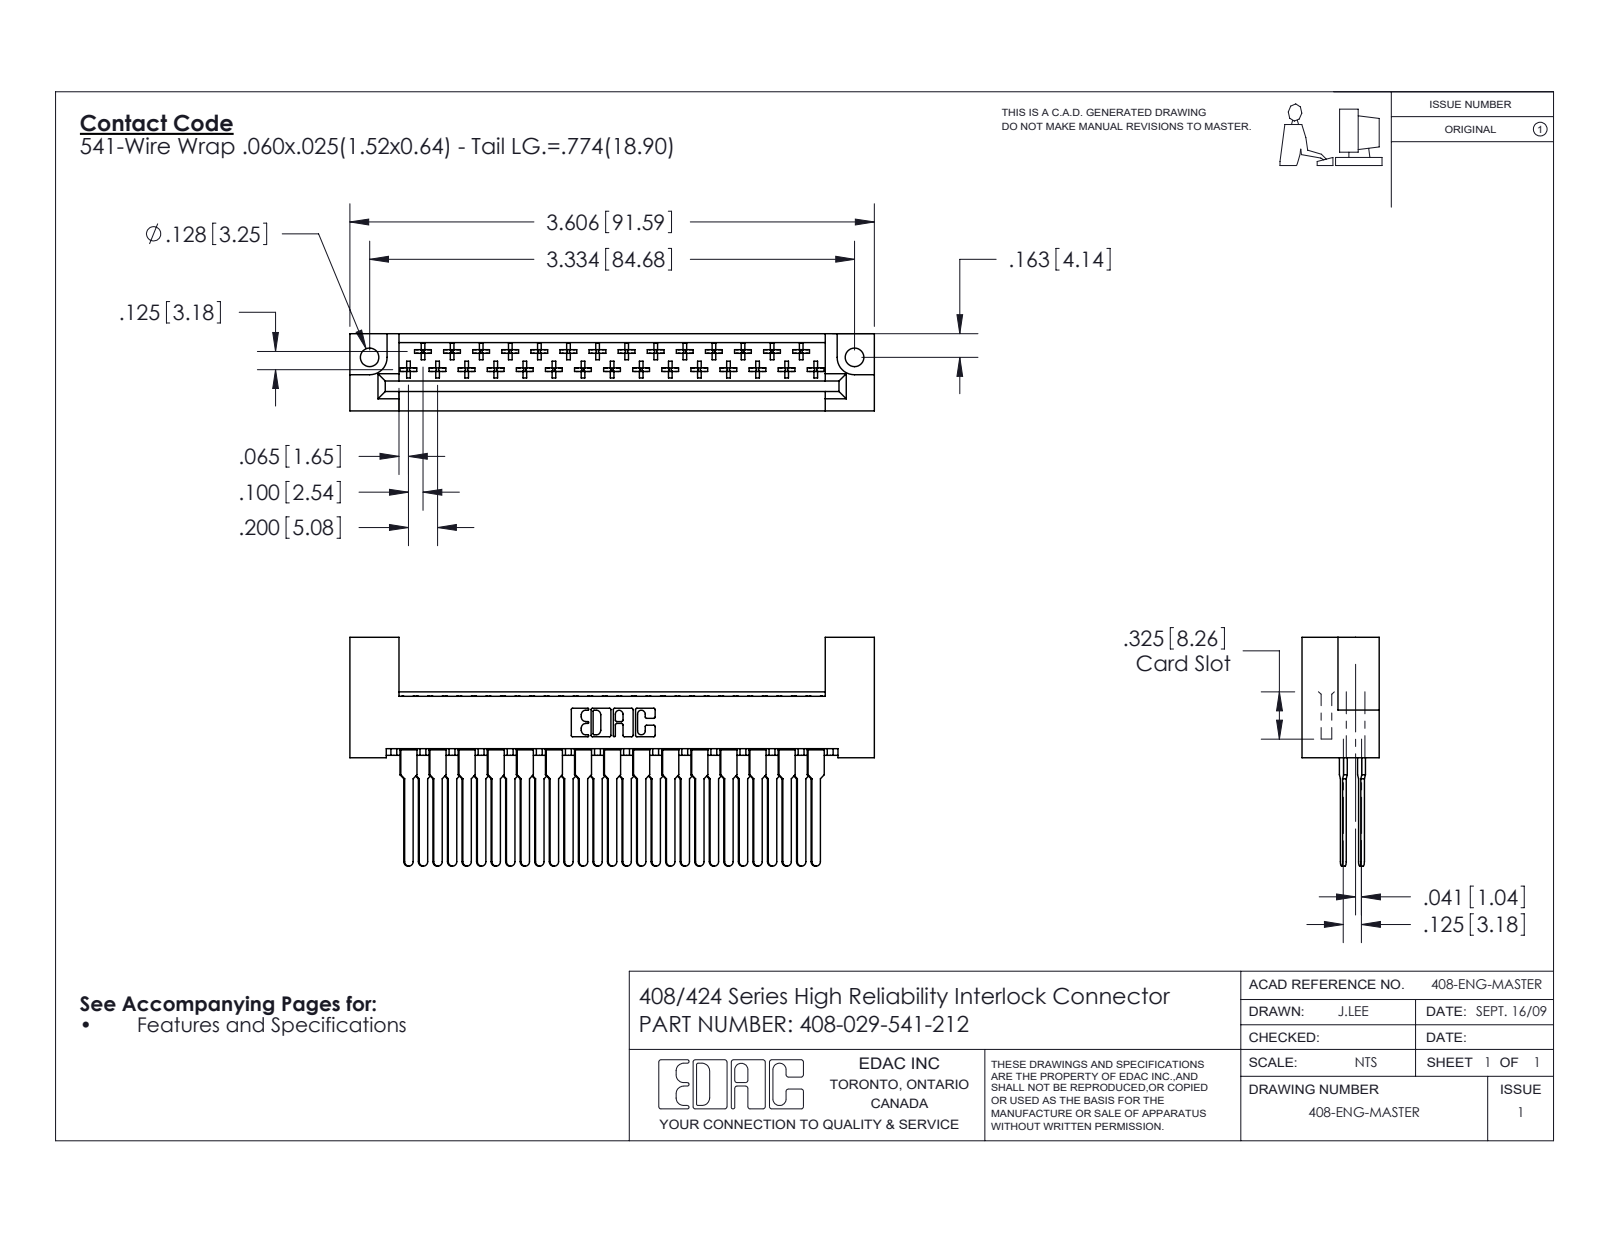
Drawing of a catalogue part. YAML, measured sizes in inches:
part_name: "408 Part_029 - 2; 408-029-541-212; 408-290-001_408-290-141"
step_written_by: "SolidWorks 2016 (CONFIG_CONTROL_DESIGN)"
units: inches
bodies: {solids: 30, faces: 1679, planar: 1249, cylindrical: 314, other: 116}
overall_size: [3.606, 1.572, 0.531]
volume: 0.743
surface_area: 23.79
round_holes:
  - {diameter: 0.128, count: 2}
partial_cylinders:
  - {radius: 0.01, count: 174}
  - {radius: 0.02, count: 31}
  - {radius: 0.03, count: 29}
  - {radius: 0.01, count: 22}
  - {radius: 0.007, count: 6}
  - {radius: 0.031, count: 6}
  - {radius: 0.026, count: 3}
  - {radius: 0.12, count: 2}
face_to_face_distances: [0.531, 0.125, 0.1, 0.025, 0.025, 0.361, 0.235, 0.259, 0.272, 0.217]
hole_center_spacings: [3.334]
